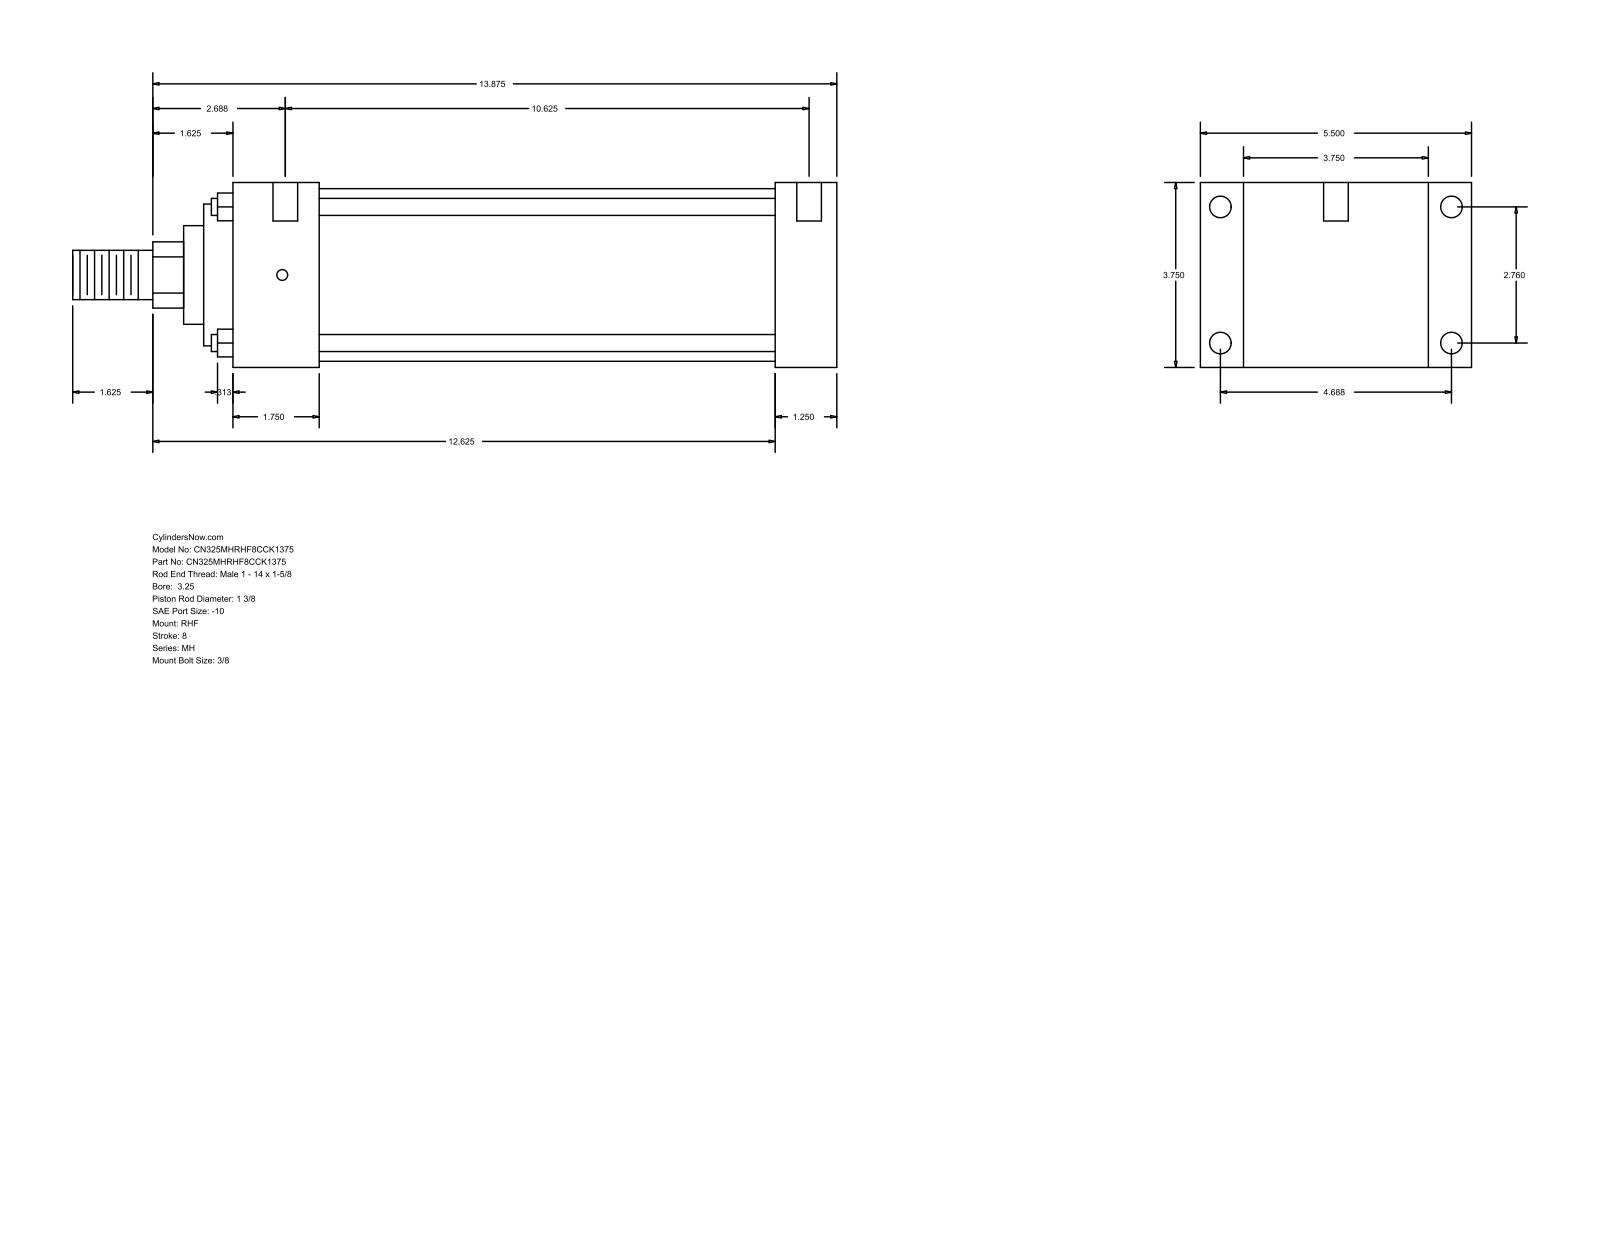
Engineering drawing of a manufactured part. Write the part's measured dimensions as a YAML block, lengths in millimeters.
part_name: "MH_RHF__0325_1.375"
step_written_by: "GSSL Pune (CONFIG_CONTROL_DESIGN)"
units: millimeters
bodies: {solids: 0, faces: 90, planar: 61, cylindrical: 29, other: 0}
overall_size: [393.7, 139.7, 95.25]
round_holes:
  - {diameter: 5.56, count: 4}
  - {diameter: 11.13, count: 4}
  - {diameter: 12.7, count: 2}
round_bosses_or_shafts:
  - {diameter: 8.76, count: 4}
  - {diameter: 88.9, count: 1}
  - {diameter: 73.03, count: 1}
  - {diameter: 50.8, count: 1}
  - {diameter: 34.92, count: 1}
  - {diameter: 25.4, count: 1}
partial_cylinders:
  - {radius: 17.06, count: 1}
face_to_face_distances: [95.24, 31.75, 22.23, 117.47, 279.41, 311.16, 139.7, 44.45, 234.96, 266.71]
hole_center_spacings: [70.1, 119.06, 138.16, 276.23, 1.59, 4.76, 269.88, 271.47]
